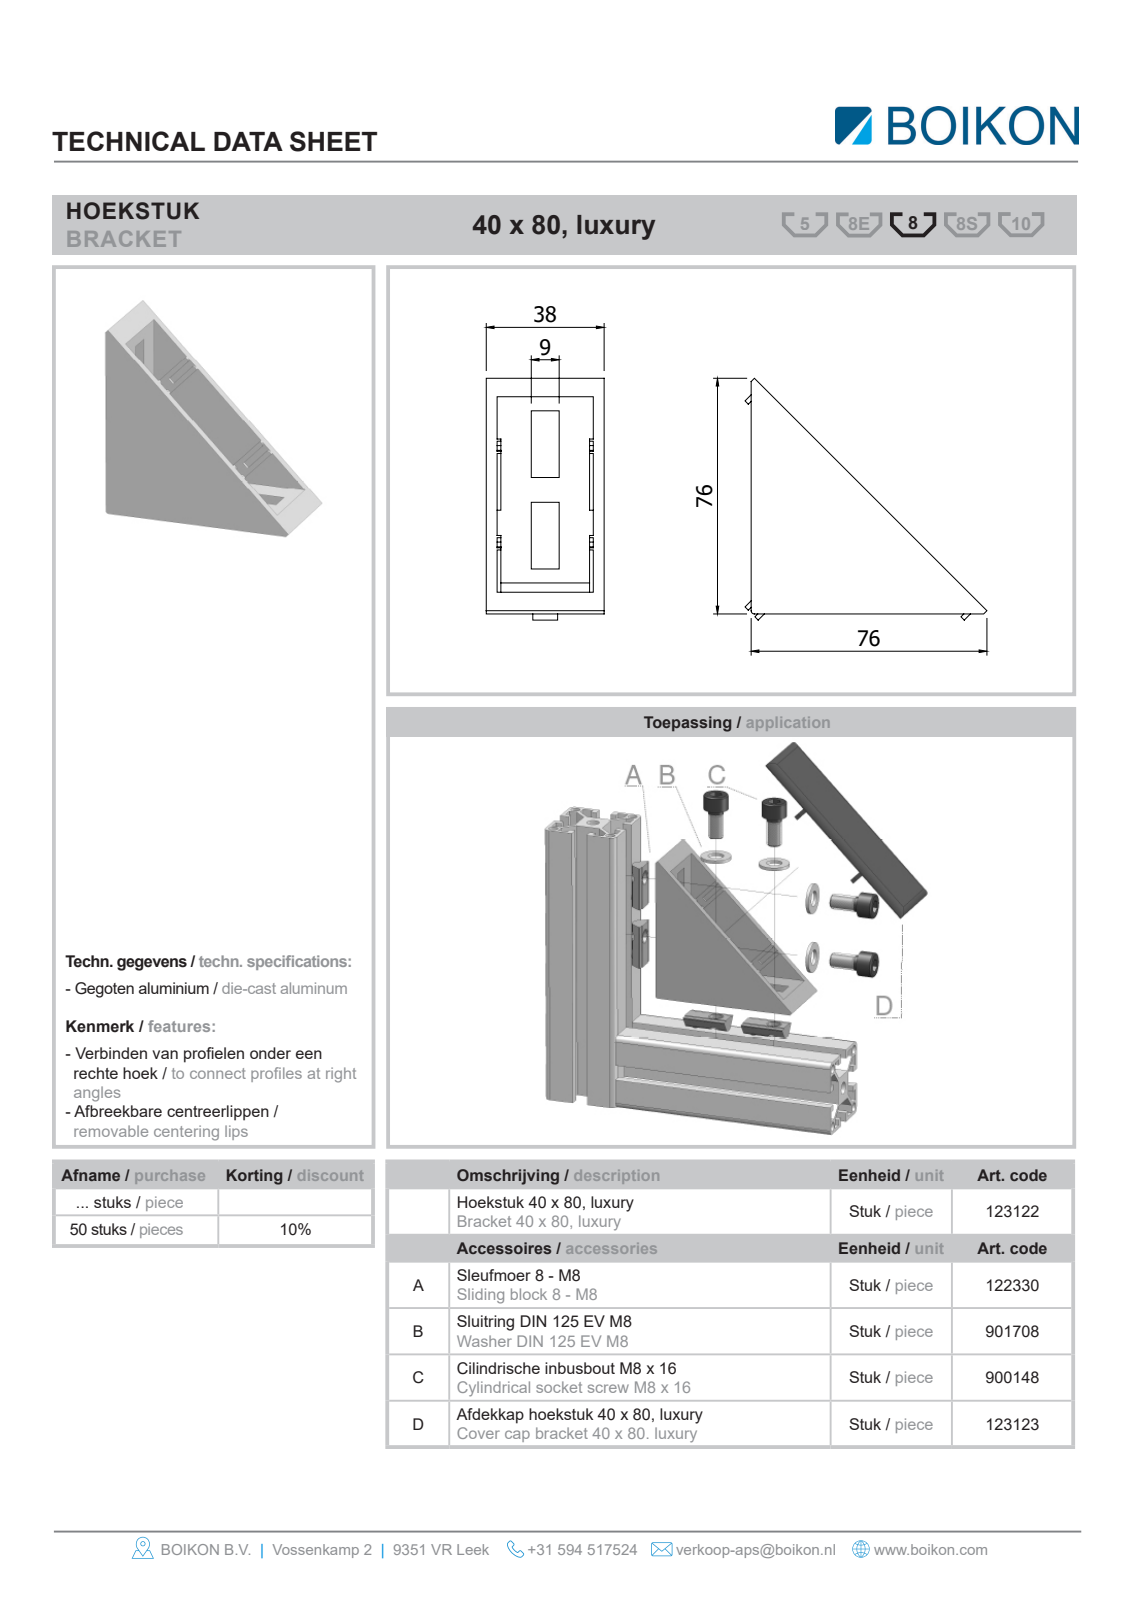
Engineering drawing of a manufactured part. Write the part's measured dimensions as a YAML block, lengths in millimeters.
part_name: "Root; 123122HOEKSTUK 40X80 LUXURYBOIKON; 123123AFDEKKAP HOEKSTUK 40X80 LUXURYBOIKON; 122330Sleufmoer 8 - M8 met kogelBOIKON (+2 more)"
step_written_by: "HiCAD 2013 1802.4 Build 509 (AUTOMOTIVE_DESIGN)"
units: millimeters
bodies: {solids: 14, faces: 378, planar: 291, cylindrical: 71, other: 16}
overall_size: [89.28, 89.28, 38]
volume: 64179
surface_area: 42569
round_holes:
  - {diameter: 8, count: 4}
  - {diameter: 8.4, count: 4}
round_bosses_or_shafts:
  - {diameter: 16, count: 4}
  - {diameter: 13, count: 4}
  - {diameter: 6.47, count: 4}
partial_cylinders:
  - {radius: 1, count: 5}
  - {radius: 0.5, count: 4}
  - {radius: 2, count: 4}
  - {radius: 3.5, count: 4}
  - {radius: 5, count: 2}
  - {radius: 3, count: 1}
face_to_face_distances: [3, 4, 3.5, 34.5, 7, 38, 1, 31, 20, 14.5]
hole_center_spacings: [28.5]
